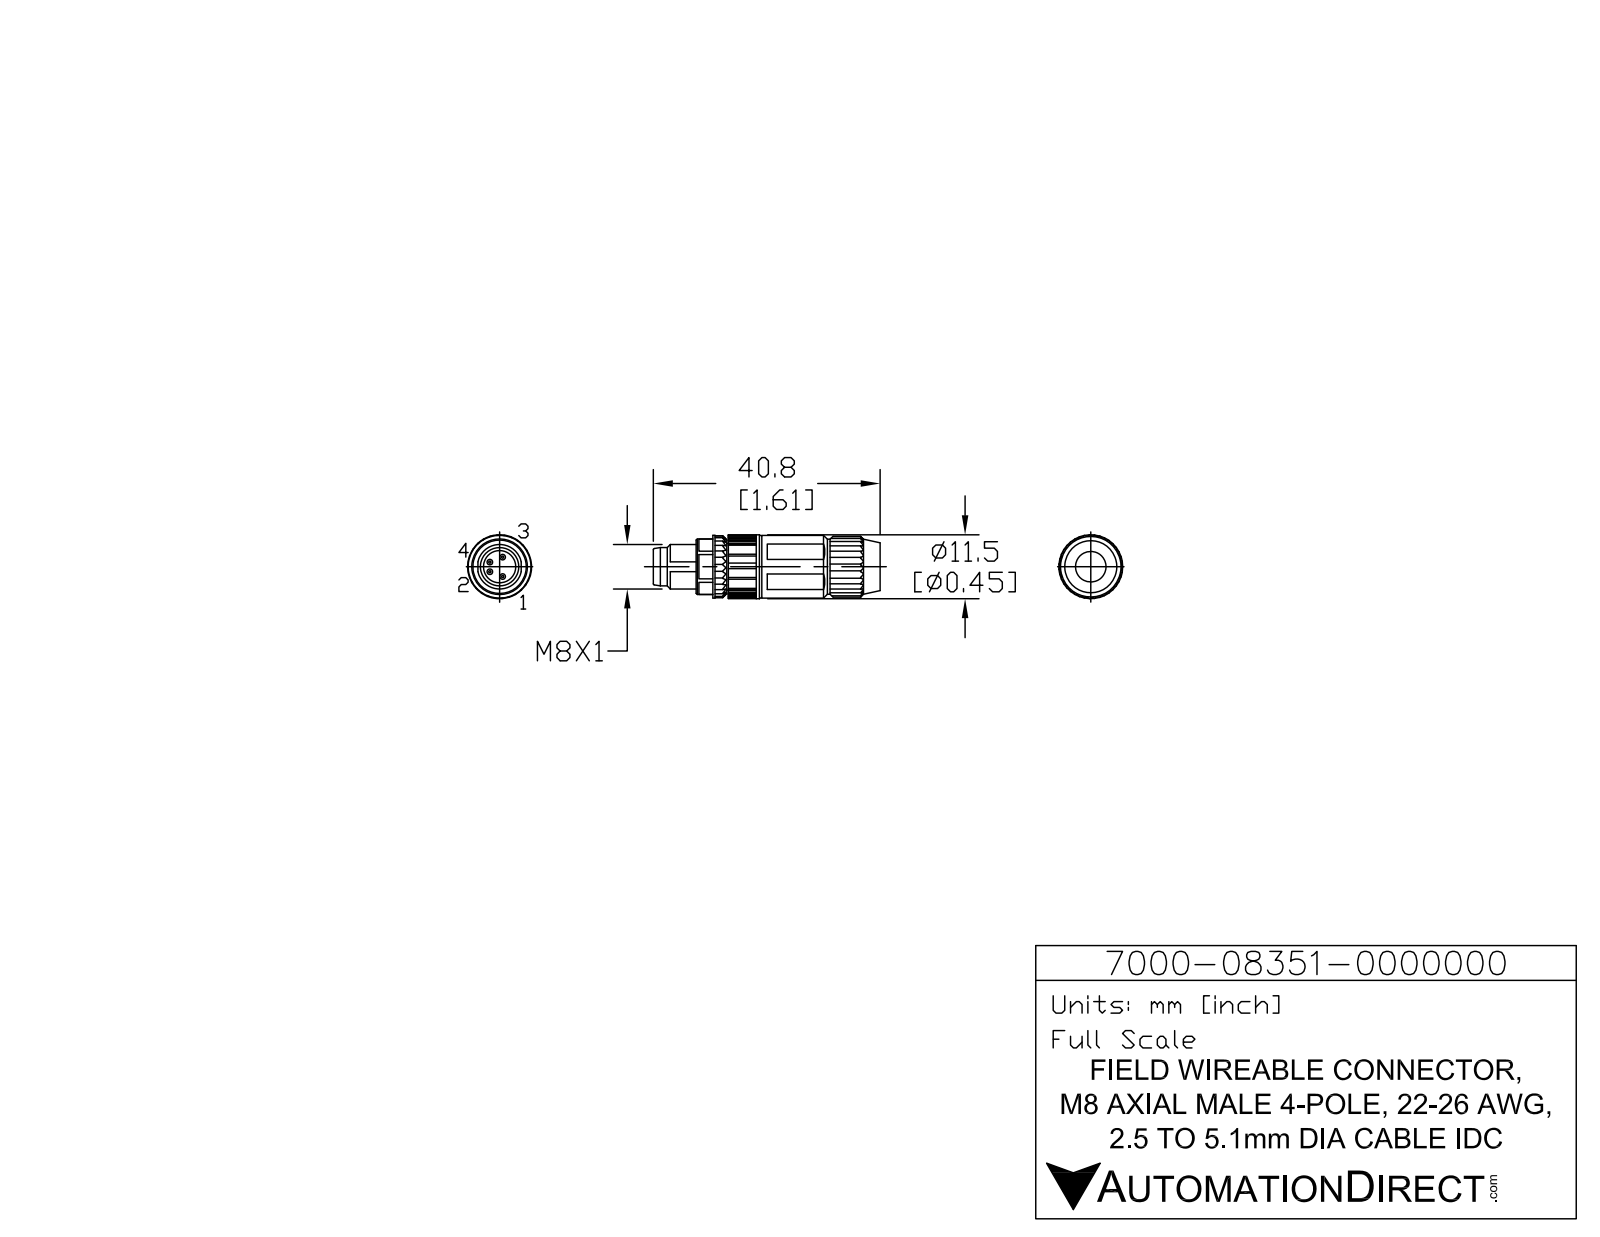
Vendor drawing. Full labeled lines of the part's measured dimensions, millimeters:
Part name (STEP PRODUCT): 7000-08351-0000000
STEP written by: SolidWorks 2015 (AUTOMOTIVE_DESIGN)
Units: millimetres
Bodies: 1 solid, 347 faces (238 planar, 60 cylindrical, 49 other)
Overall size (bounding box): 40.8 × 11.5 × 11.5
Volume: 2 625 mm³ · Surface area: 2 534 mm²
Round holes (diameter × count): ⌀5.6 ×1, ⌀5.71 ×1
Round bosses / shafts (diameter × count): ⌀0.9 ×4, ⌀11.5 ×1, ⌀10.27 ×1, ⌀10.24 ×1, ⌀7.86 ×1, ⌀6.72 ×1
Main face-to-face distances: 3.23, 29.7, 32.93, 8.88, 20, 9.7, 12.93, 30.5, 10.5, 0.8
